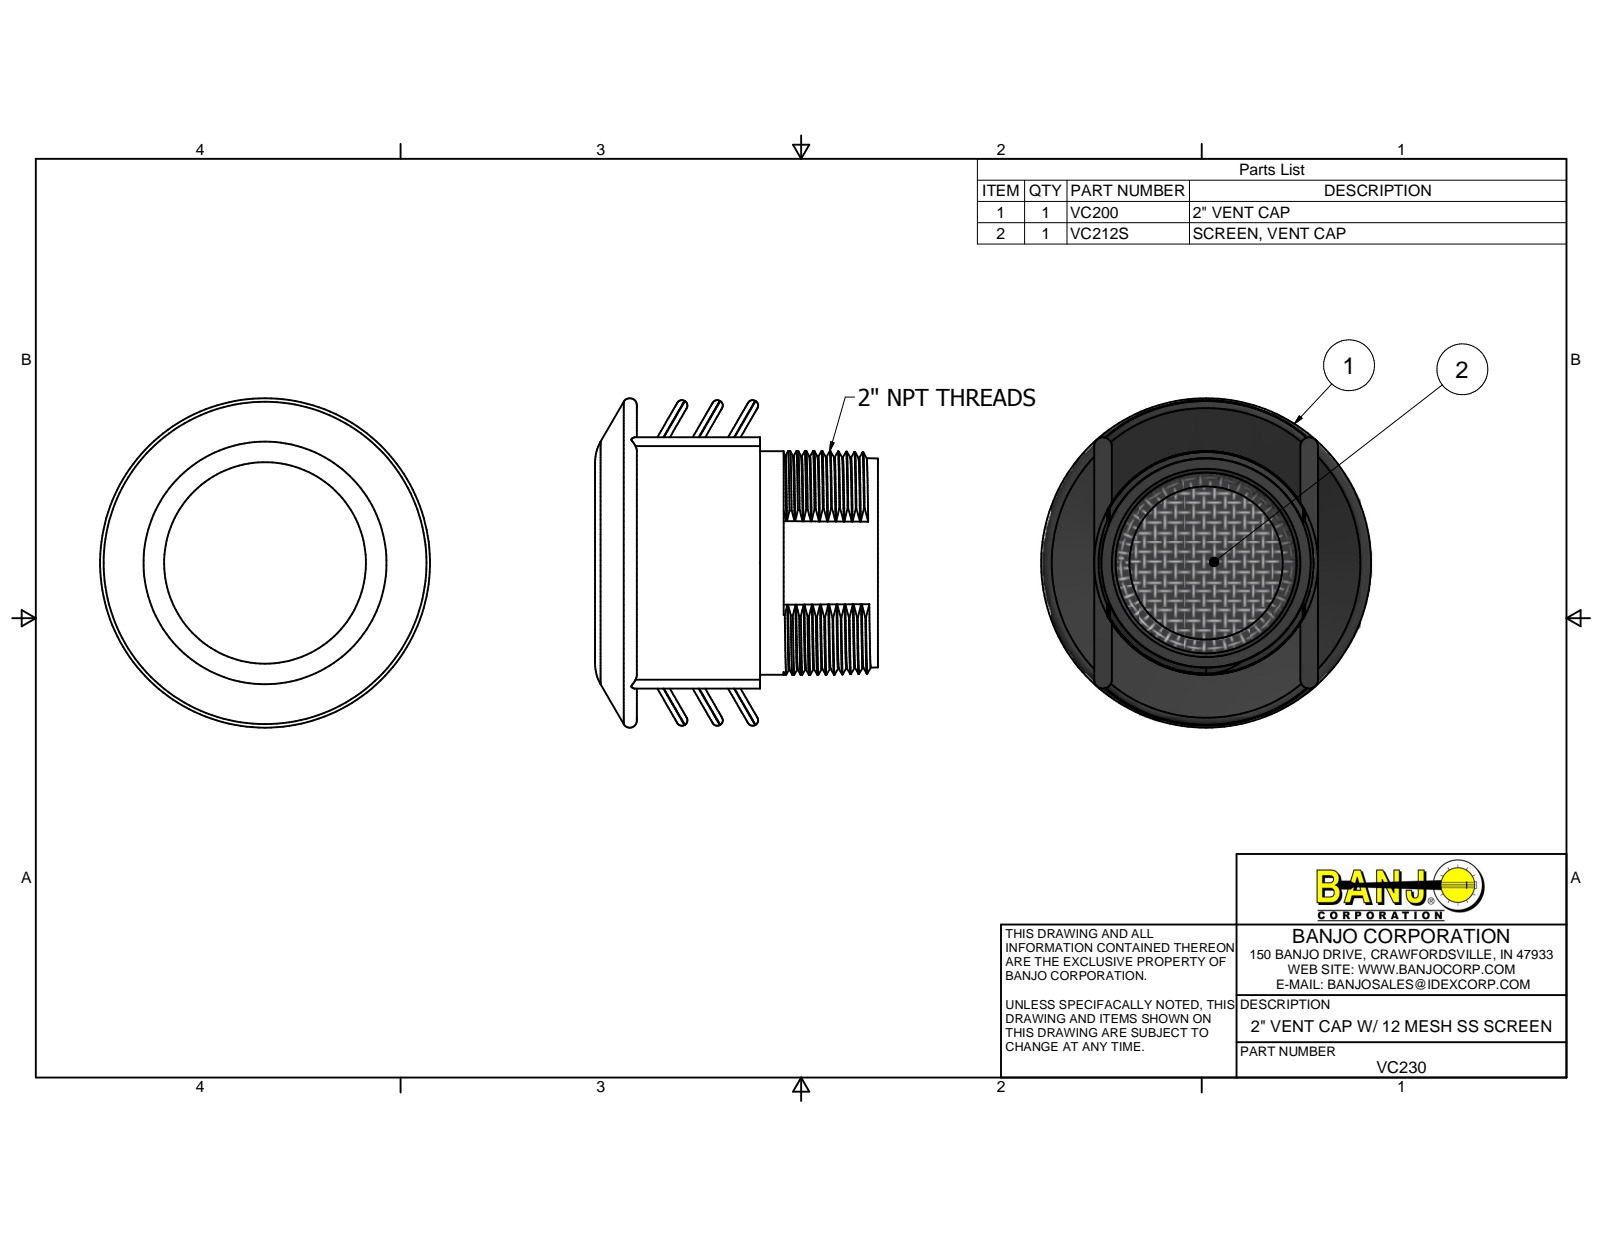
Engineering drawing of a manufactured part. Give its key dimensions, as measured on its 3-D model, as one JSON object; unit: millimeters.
{"part_name": "VC200; VC212S; VC230", "step_written_by": "Autodesk Inventor 2016 (AUTOMOTIVE_DESIGN)", "units": "millimeters", "bodies": {"solids": 2, "faces": 200, "planar": 95, "cylindrical": 24, "other": 81}, "overall_size": [88.9, 88.9, 76.2], "volume_mm3": 102667, "surface_area_mm2": 72730, "round_holes": [[50.8, 1]], "round_bosses_or_shafts": [[60.32, 1]], "partial_cylinders_radius": [[37.79, 6], [2.38, 4], [15.73, 1]], "face_to_face_distances": [8.25, 2.92, 16.5, 11.17, 5.33, 60.32, 3.81, 4.76, 55.56, 19.42]}
